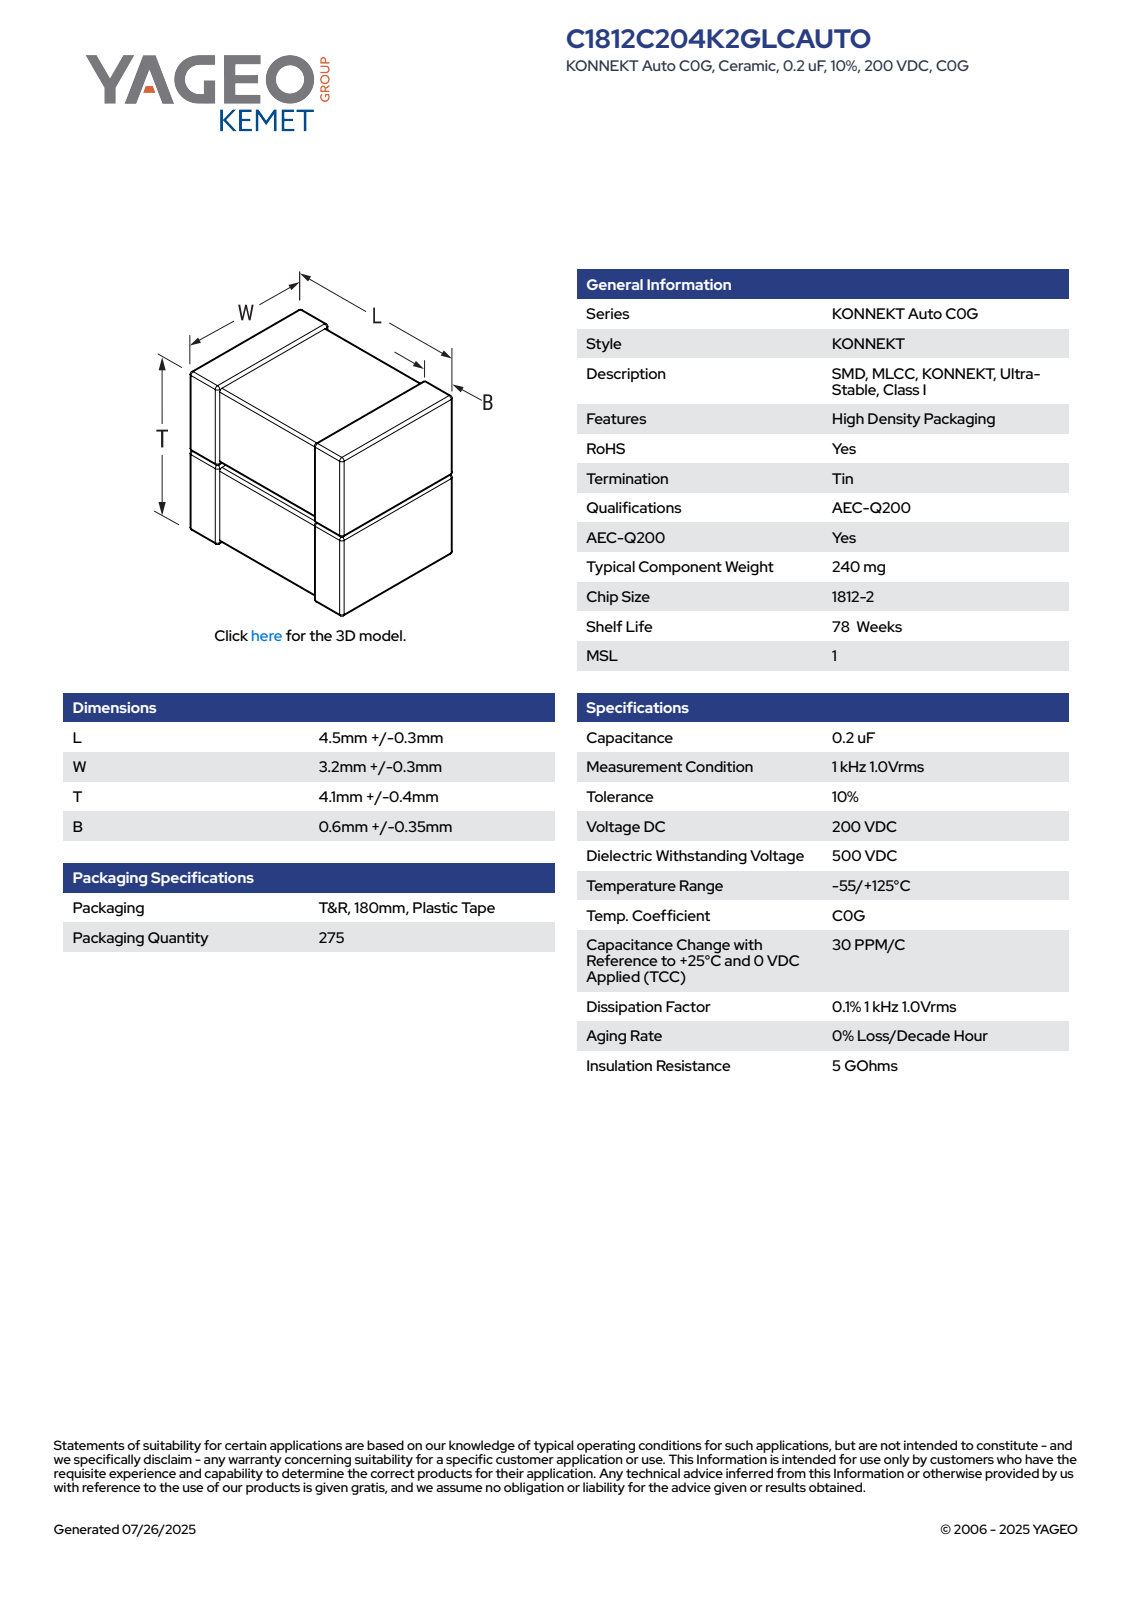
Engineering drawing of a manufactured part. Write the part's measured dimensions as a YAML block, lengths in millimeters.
part_name: "CCSS_K2T_1812-2_L4.8W3.5B0.95T4.5"
step_written_by: "SolidWorks 2020 (AUTOMOTIVE_DESIGN)"
units: millimeters
bodies: {solids: 4, faces: 197, planar: 81, cylindrical: 84, other: 32}
overall_size: [4.8, 4.5, 3.5]
volume: 71
surface_area: 128
face_to_face_distances: [2.11, 2.25, 4.8, 3.43, 3.36, 2.18, 2.32, 4.43, 4.36, 3.5]
